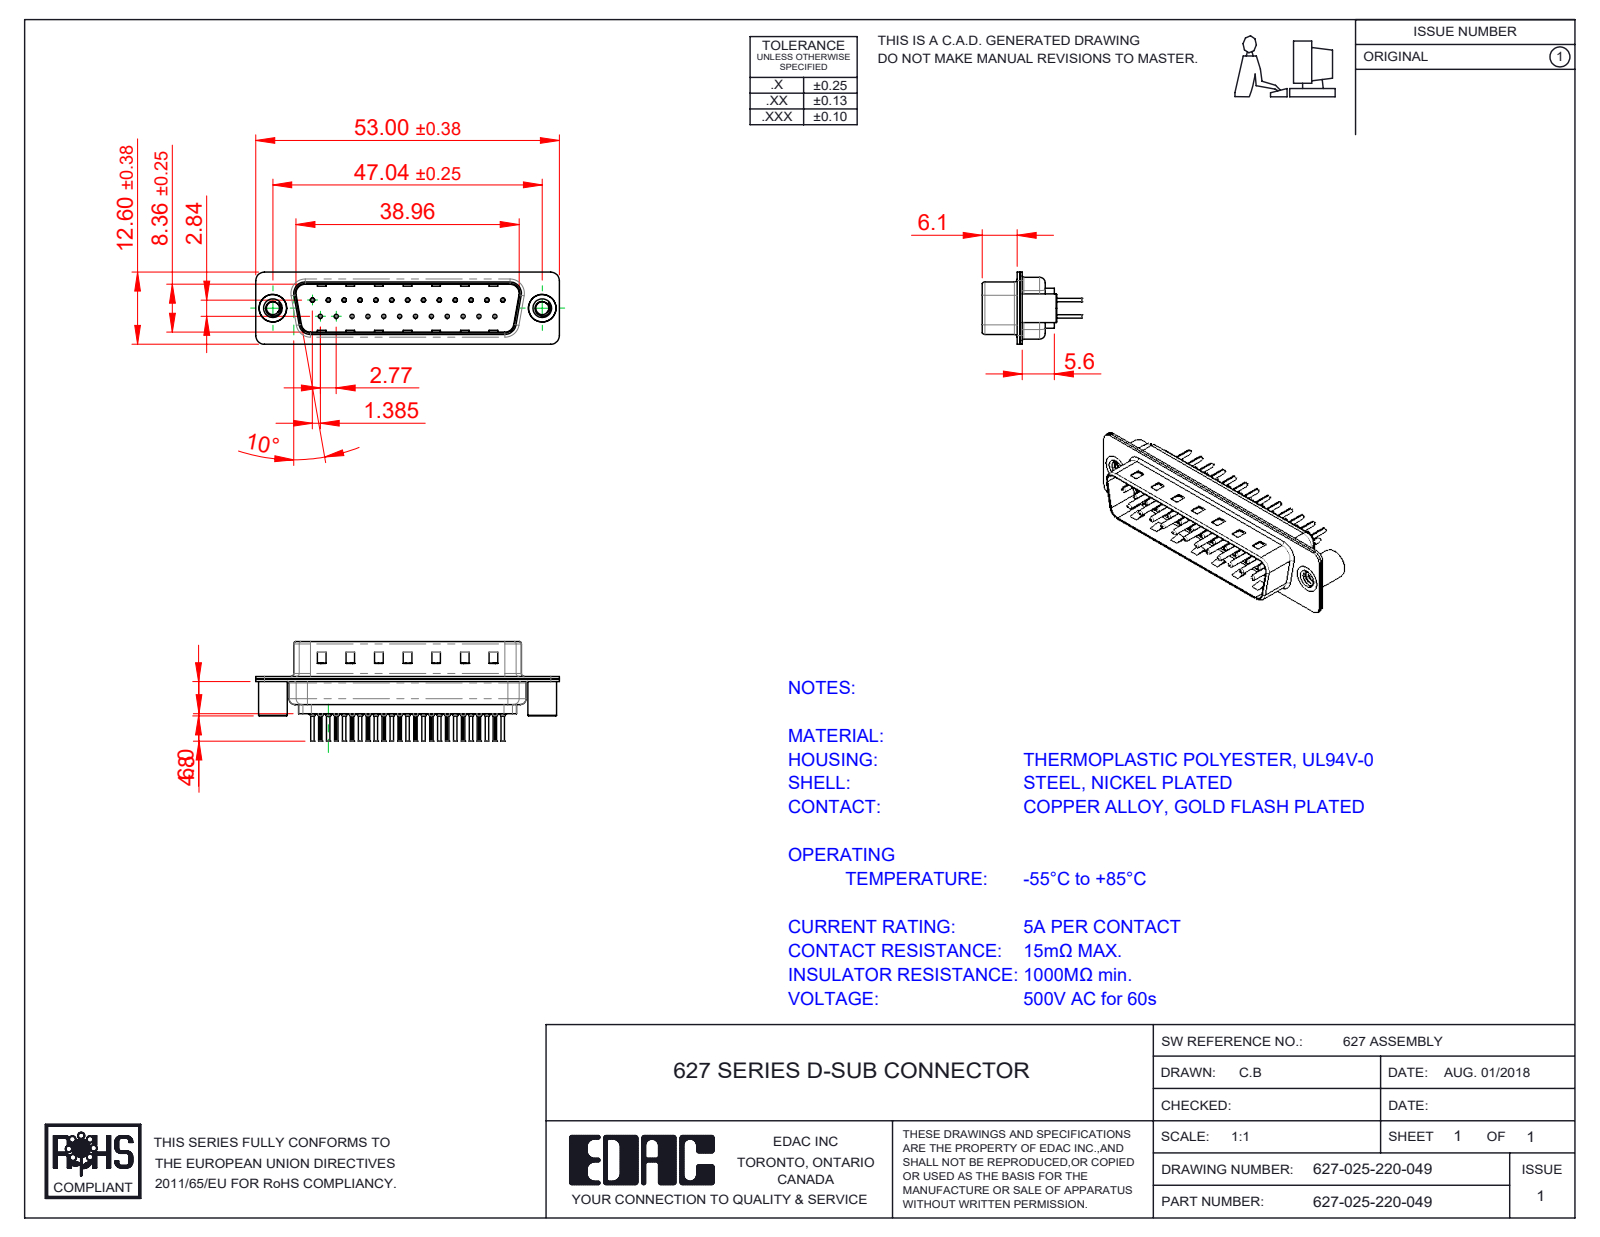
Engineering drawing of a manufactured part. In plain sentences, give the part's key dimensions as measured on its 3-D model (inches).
The part is named "627 Housing_25 LP; 627 Contact Row 2_20L; 627 Shell Rear_25 Contacts; 627 Shell Front_25 Contacts (+3 more)". Its 3-D file was written by "SolidWorks 2020 (CONFIG_CONTROL_DESIGN)". It is 30 solids with 2848 faces: 771 planar, 1082 cylindrical and 995 other. Overall it measures 2.087 by 0.681 by 0.496 inches. Its volume is 0.17 cubic inches and its surface area 12.39 square inches. Round holes: 25 of diameter 0.008, 25 of diameter 0.014, 25 of diameter 0.043, 25 of diameter 0.063, 2 of diameter 0.089, 2 of diameter 0.157, 2 of diameter 0.189. Round bosses or shafts: 25 of diameter 0.079, 25 of diameter 0.059, 25 of diameter 0.03, 25 of diameter 0.024, 2 of diameter 0.197, 2 of diameter 0.193. Partial cylindrical surfaces (rounded edges, fillets, slot ends): 50 of radius 0.004, 16 of radius 0.059, 12 of radius 0.079, 8 of radius 0.02, 8 of radius 0.063, 4 of radius 0.01, 4 of radius 0.024, 4 of radius 0.026. The main face-to-face distances are 0.016, 0.018, 0.032, 0.377, 0.345, 0.035, 0.059, 0.256, 0.055, 0.238. The hole center spacings are 0.124, 0.327, 0.109, 0.218, 0.436, 0.654, 0.198, 0.198.
